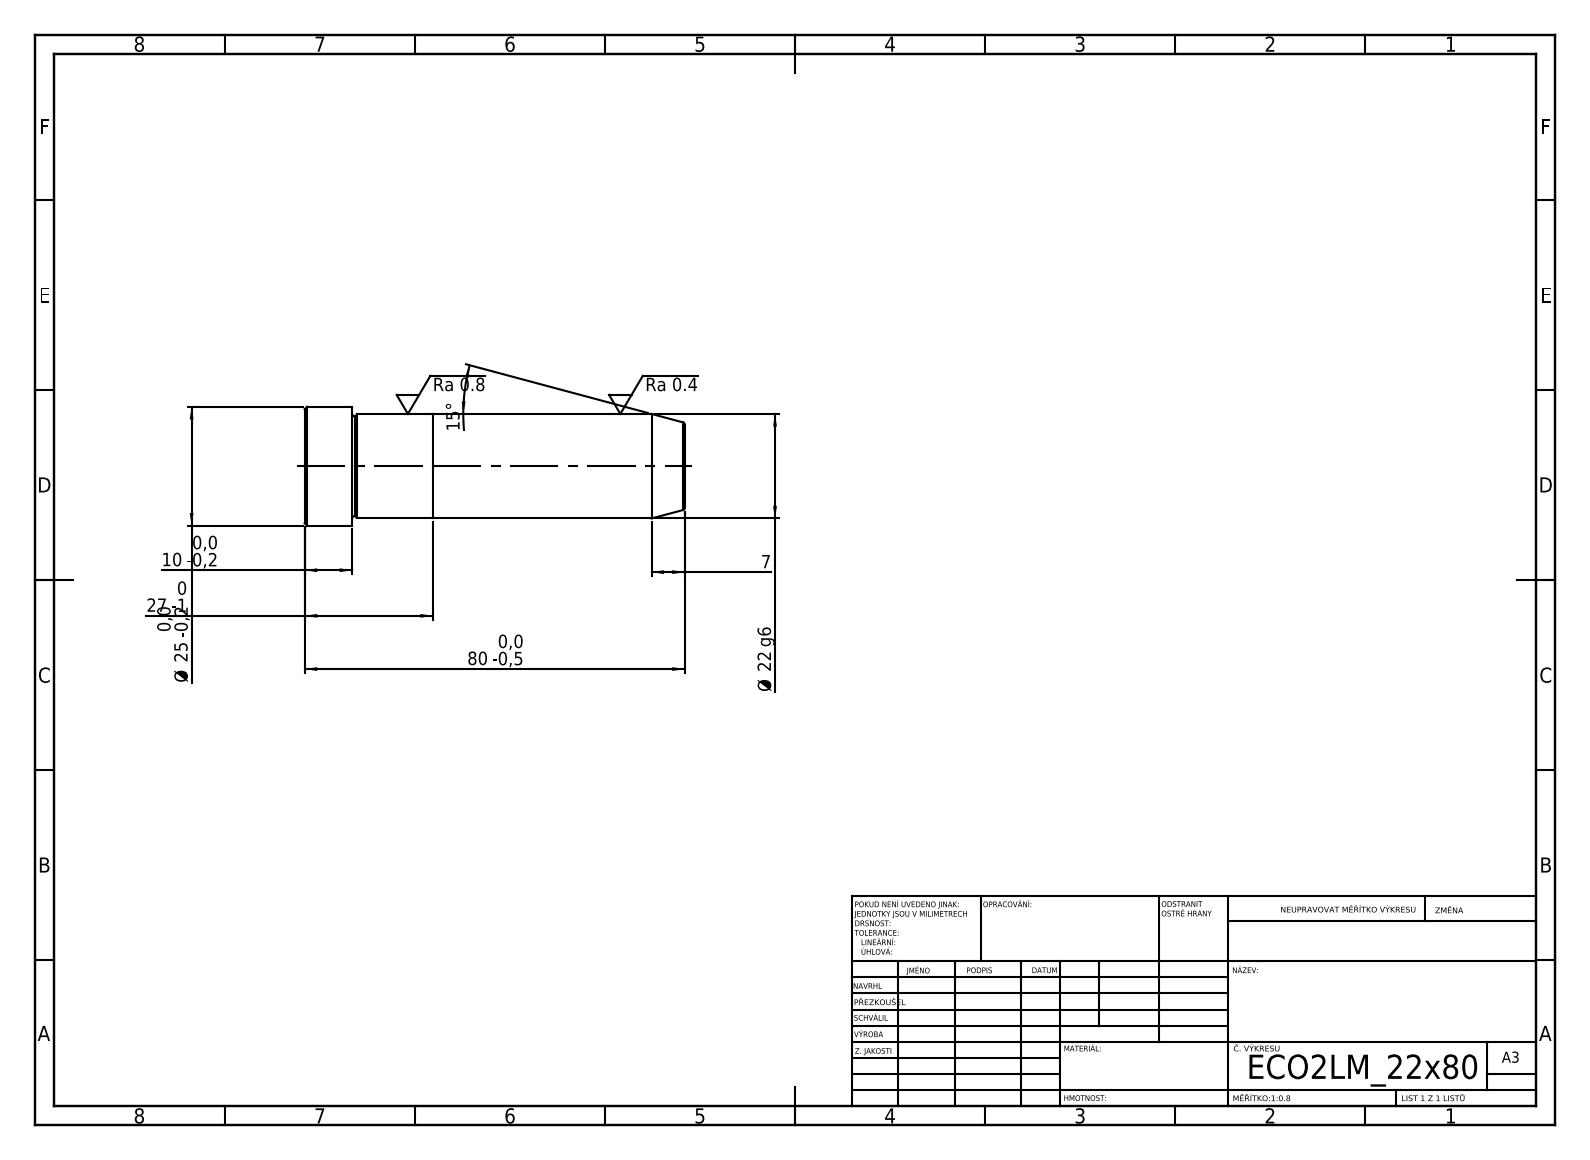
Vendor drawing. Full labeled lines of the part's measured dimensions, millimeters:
STEP written by: SolidWorks 2019 (CONFIG_CONTROL_DESIGN)
Units: millimetres
Bodies: 2 solids, 21 faces (5 planar, 6 cylindrical, 10 other)
Overall size (bounding box): 80 × 25 × 25
Volume: 31 052 mm³ · Surface area: 7 228 mm²
Round bosses / shafts (diameter × count): ⌀25 ×1, ⌀22 ×1
Main face-to-face distances: 27, 53, 80, 70, 17, 10
